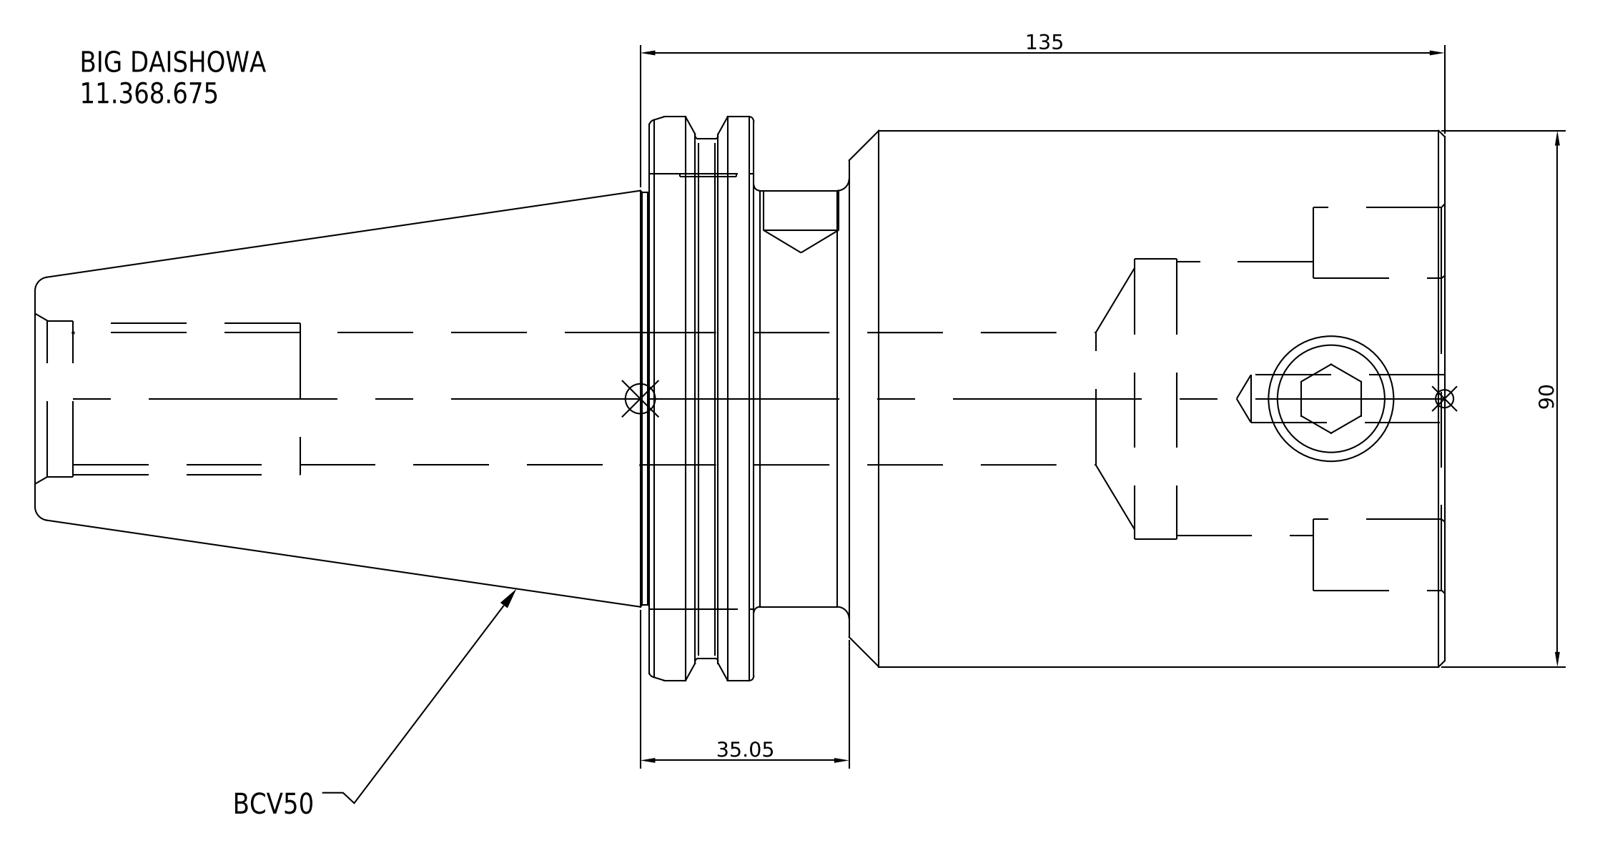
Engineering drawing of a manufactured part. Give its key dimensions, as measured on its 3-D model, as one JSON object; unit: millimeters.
{"part_name": "11.368.675", "step_written_by": "SolidWorks 2021 (CONFIG_CONTROL_DESIGN)", "units": "millimeters", "bodies": {"solids": 1, "faces": 16, "planar": 7, "cylindrical": 6, "other": 3}, "overall_size": [236.6, 98.43, 98.43], "volume_mm3": 1079000, "surface_area_mm2": 74307, "round_bosses_or_shafts": [[98.43, 1], [91.29, 1], [90, 1], [69.85, 1]], "face_to_face_distances": [133.5, 115.95, 17.55, 100, 15.95, 33.5, 236.6, 136.6, 120.65, 103.1]}
